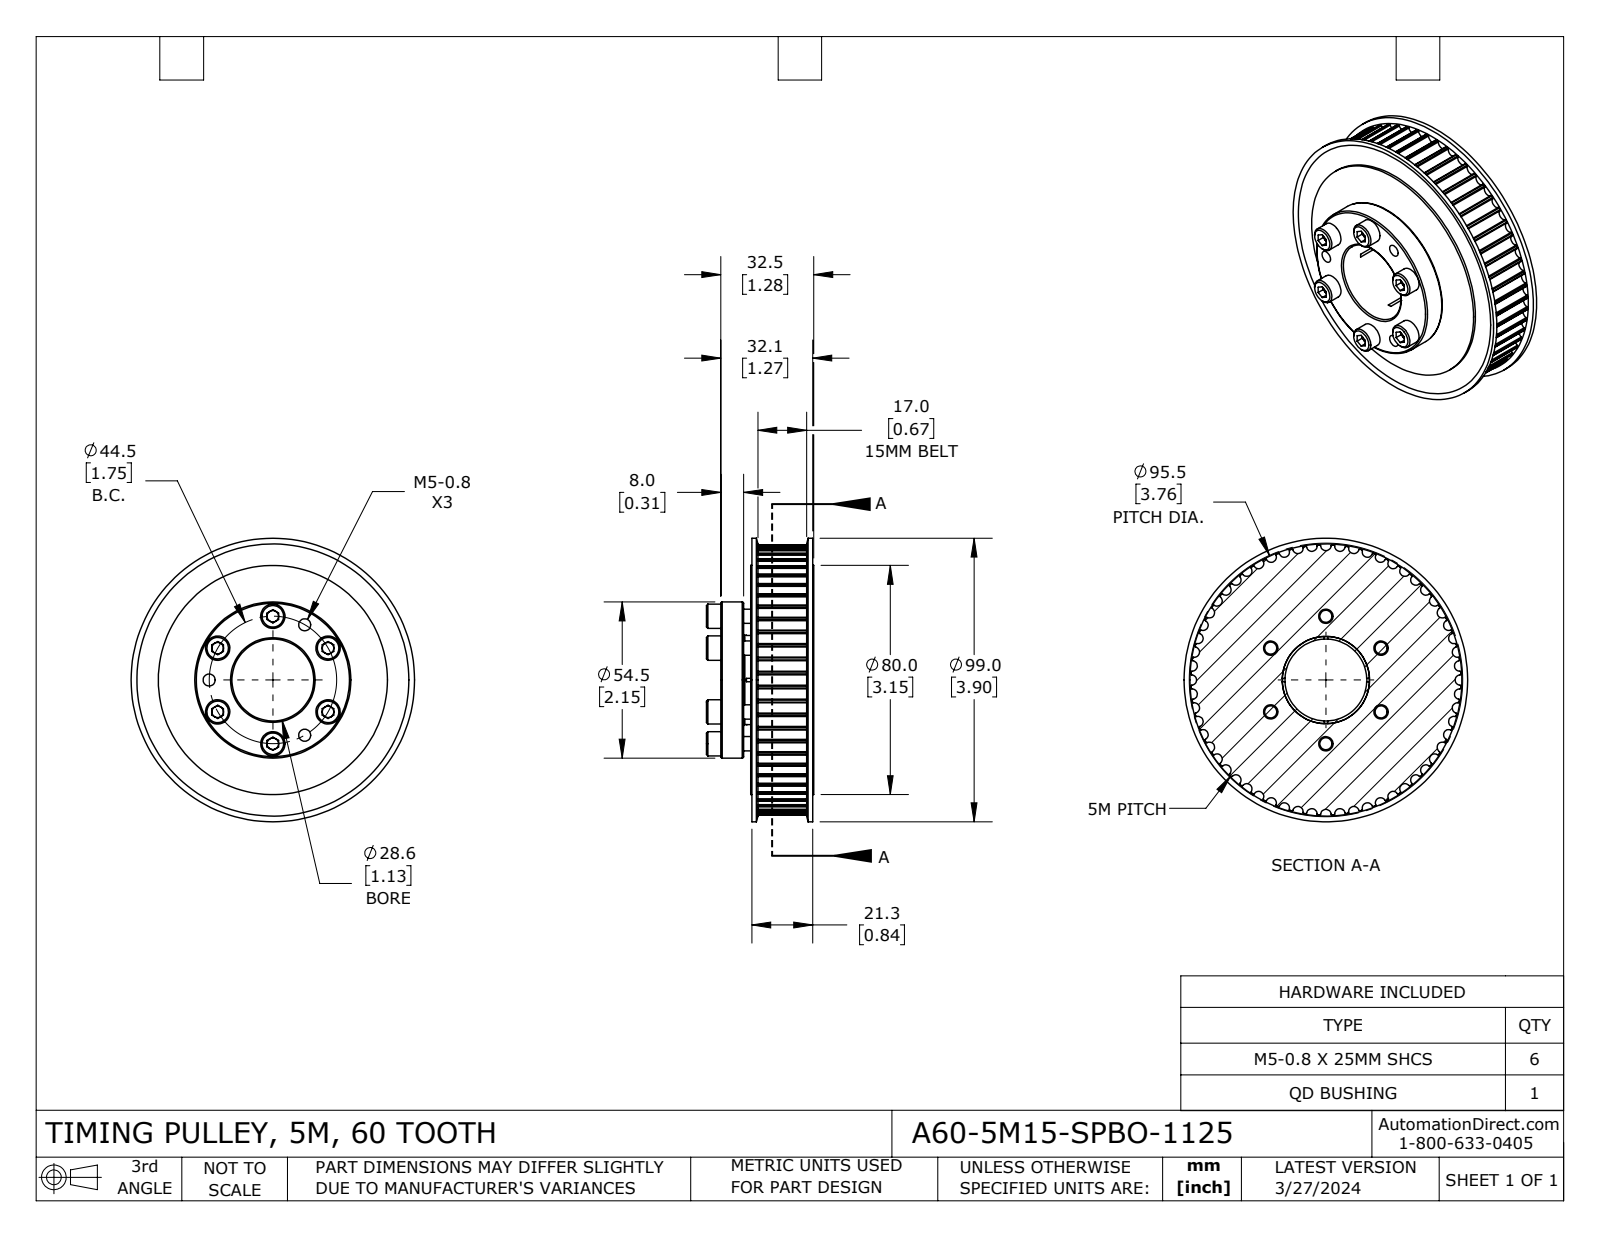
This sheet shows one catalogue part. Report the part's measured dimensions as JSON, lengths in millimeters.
{"part_name": "A60-5M15-SPBO-1125", "step_written_by": "SolidWorks 2021 (CONFIG_CONTROL_DESIGN)", "units": "millimeters", "bodies": {"solids": 10, "faces": 553, "planar": 116, "cylindrical": 375, "other": 62}, "overall_size": [99, 99, 37.5], "volume_mm3": 147126, "surface_area_mm2": 49535, "round_holes": [[4.2, 9], [5.5, 6], [28.57, 1], [28.58, 1], [31.18, 1], [80, 1]], "round_bosses_or_shafts": [[8.5, 6], [5, 6], [99, 1], [54.5, 1], [31.17, 1]], "partial_cylinders_radius": [[0.3, 120], [1.82, 60], [47.17, 1]], "face_to_face_distances": [2.5, 19.5, 22, 0.9, 21.1, 1.6, 18.6, 17, 20.2, 13], "hole_center_spacings": [22.25, 38.54, 44.5, 31.47, 42.99, 11.52, 38.53, 11.51]}
